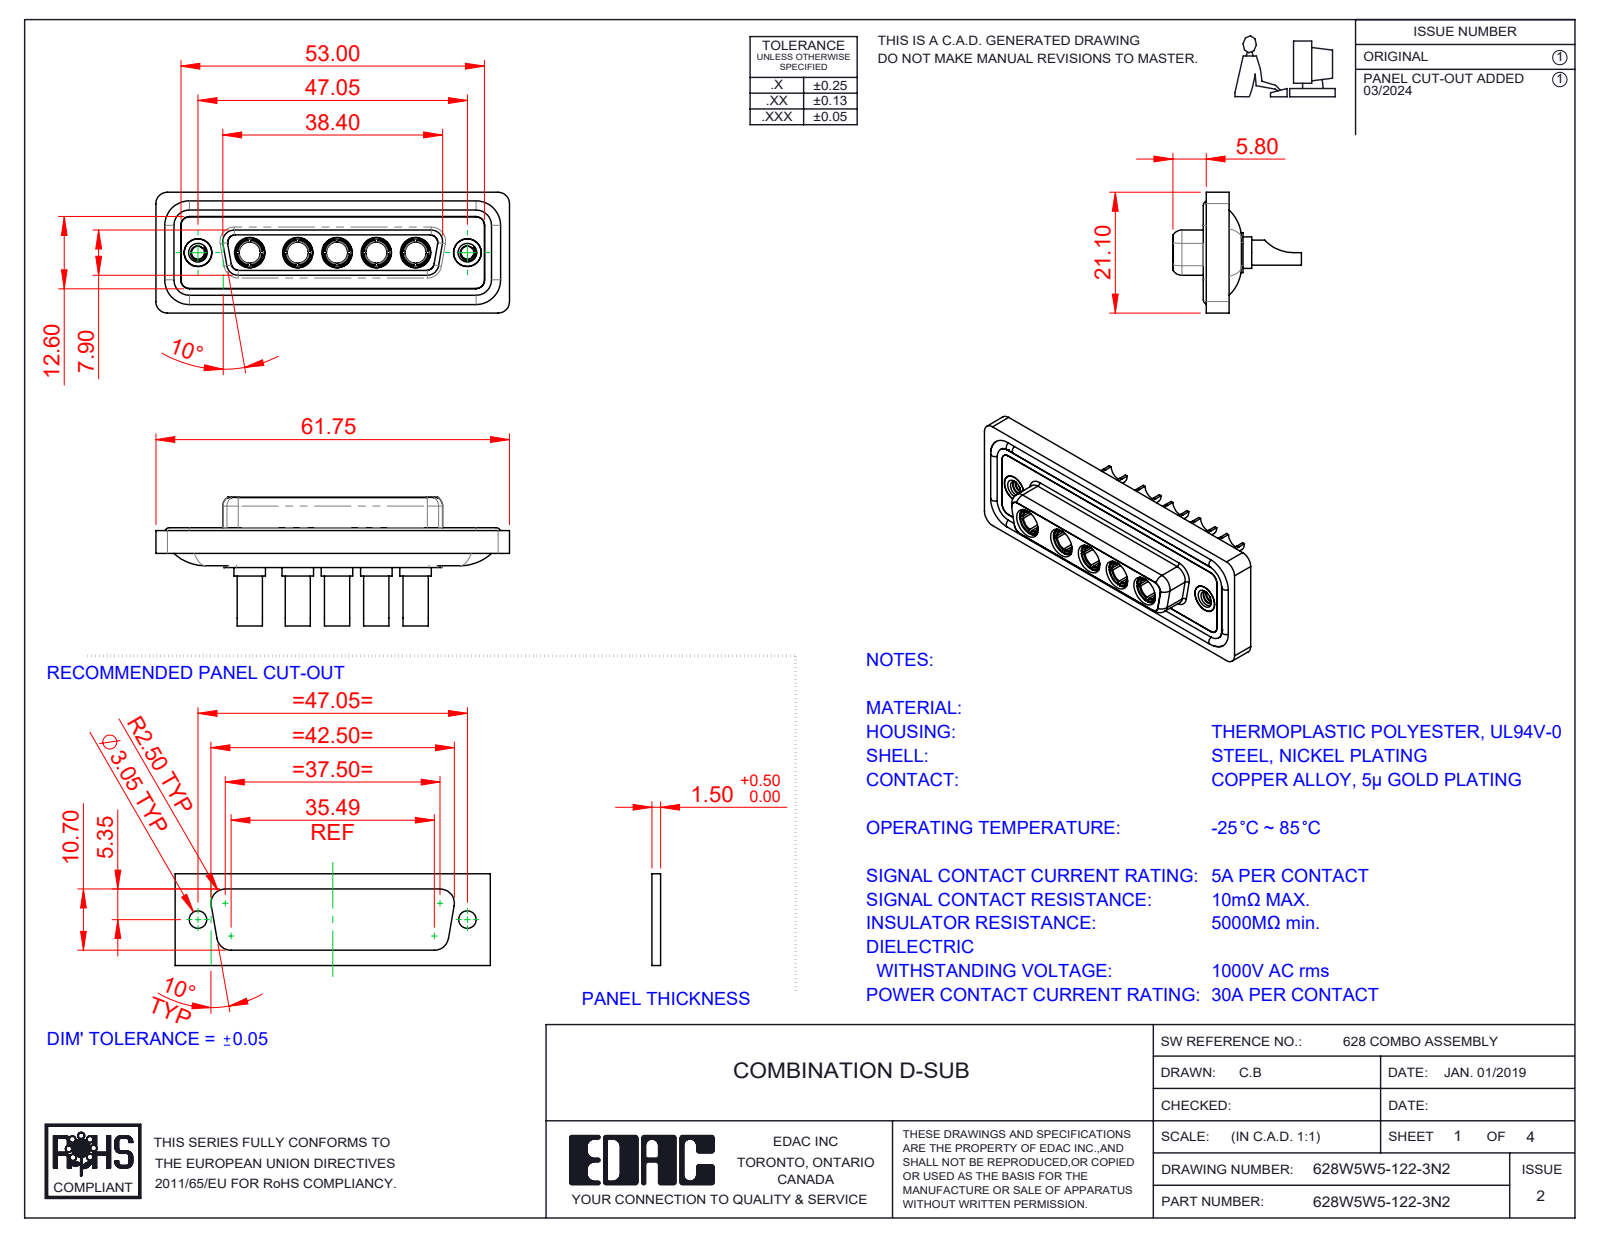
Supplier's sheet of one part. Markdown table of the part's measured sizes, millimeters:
| quantity | value |
| --- | --- |
| part name | 628Combo Housing_5W5; 628Combo Waterproof Housing_25 Contacts; 628Combo Threaded Rivet_2; Power Socket_30A SC (+3 more) |
| STEP written by | SolidWorks 2023 (CONFIG_CONTROL_DESIGN) |
| units | millimeters |
| bodies | 17 solids, 786 faces (265 planar, 318 cylindrical, 203 other) |
| overall size | 61.75 × 22.45 × 21.1 |
| volume | 8 293 mm³ |
| surface area | 13 953 mm² |
| round holes (diameter × count) | 4.85 × 7, 3.5 × 5, 3.7 × 5, 5.3 × 5, 2.26 × 2, 4 × 2, 4.05 × 2, 5 × 2 |
| round bosses / shafts (diameter × count) | 5.5 × 5, 5.2 × 5, 4.96 × 5, 4.75 × 5, 4.4 × 5, 3.75 × 5, 1.6 × 4, 4.95 × 2 |
| partial cylindrical surfaces (radius × count) | 1.5 × 22, 2 × 18, 1.35 × 8, 1.6 × 8, 2.1 × 5, 0.25 × 4, 0.5 × 4, 0.6 × 4 |
| main face-to-face distances | 0.4, 1.8, 7.45, 5.65, 0.5, 7.05, 6.6, 1.6, 1.1, 2.9 |
| hole center spacings | 6.86, 9.04, 13.72, 38.01, 8.39, 15.25, 15.9, 17.43 |
